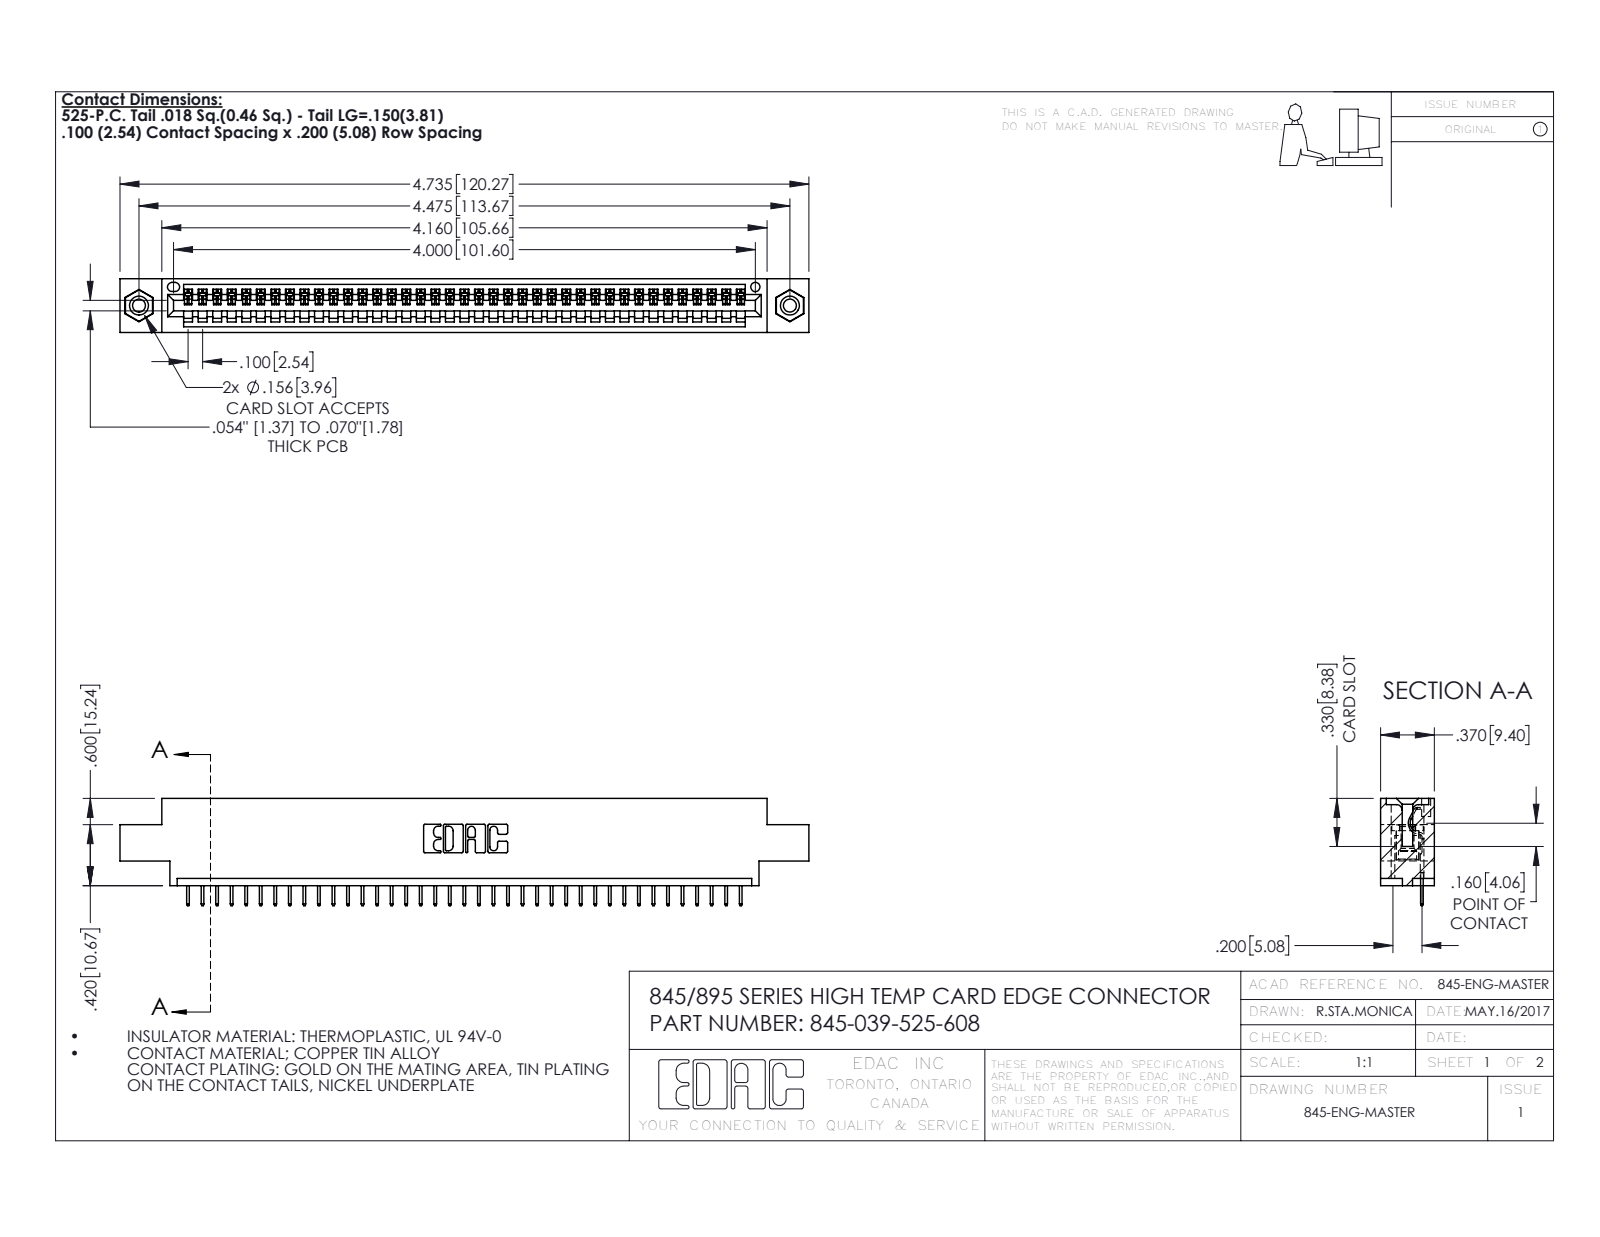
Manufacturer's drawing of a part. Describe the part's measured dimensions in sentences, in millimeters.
The part is named "845 Part_0.170 Offset - 0.156 Dia-TI; 345-292-001_345-293-125; 345-250-001_345-250-003-102; 845-039-525-608". Its 3-D file was written by "SolidWorks 2020 (CONFIG_CONTROL_DESIGN)". It is 42 solids with 2608 faces: 1910 planar, 682 cylindrical and 16 other. Overall it measures 120.3 by 18.7 by 9.4 millimeters. Its volume is 11 100 cubic millimeters and its surface area 14 350 square millimeters. Round holes: 2 of diameter 2.3, 2 of diameter 3.2, 2 of diameter 4, 1 of diameter 1.6. Round bosses or shafts: 2 of diameter 3.9. Partial cylindrical surfaces (rounded edges, fillets, slot ends): 78 of radius 0.2, 22 of radius 0.3, 6 of radius 0.2, 6 of radius 0.8, 3 of radius 0.7, 2 of radius 0.8, 2 of radius 1, 1 of radius 0.4. The main face-to-face distances are 1.8, 7.6, 9.4, 5.1, 2.5, 6.9, 0.6, 5.7, 1.8, 4.4. The hole center spacings are 6.9, 107.7, 113.7.
